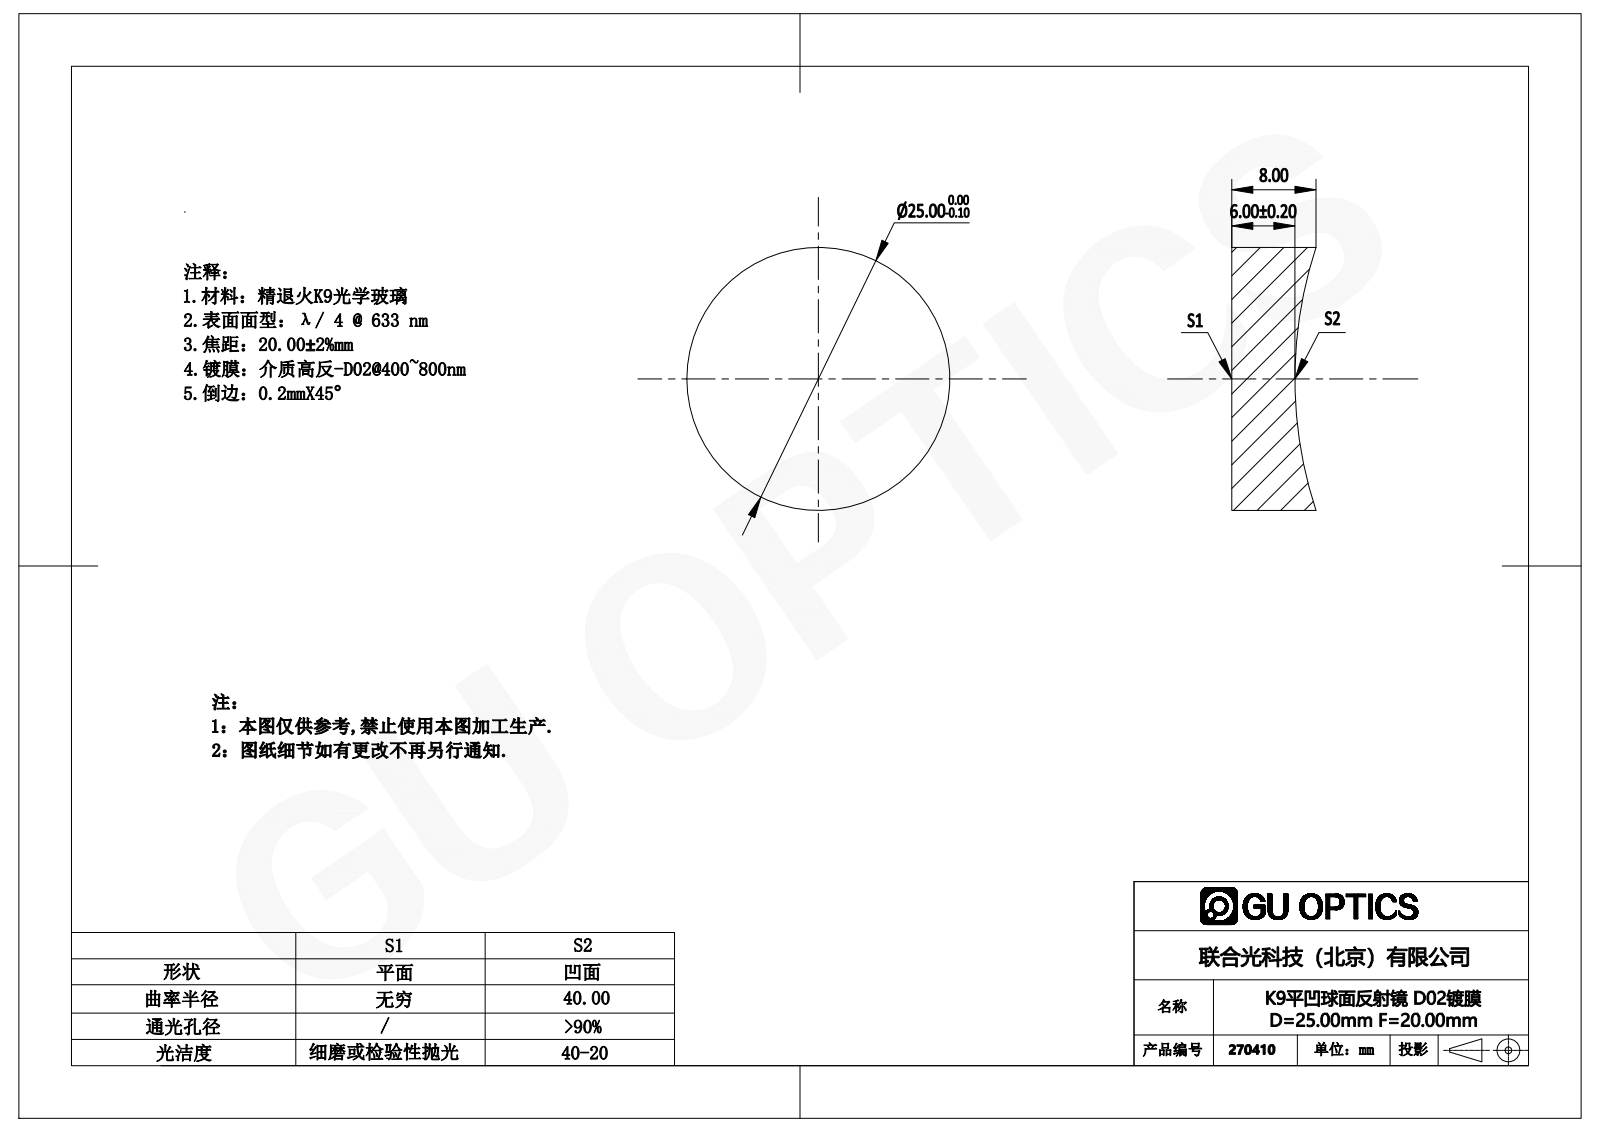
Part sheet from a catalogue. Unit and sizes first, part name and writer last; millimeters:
Units: millimetres
Overall size (bounding box): 25 × 25 × 8
Round bosses / shafts (diameter × count): ⌀25 ×1
Volume: 3 433 mm³ · Surface area: 1 623 mm²
Bodies: 1 solid, 5 faces (1 planar, 2 cylindrical, 2 other)
Part name (STEP PRODUCT): 270020
STEP written by: SolidWorks 2016 (AUTOMOTIVE_DESIGN)
